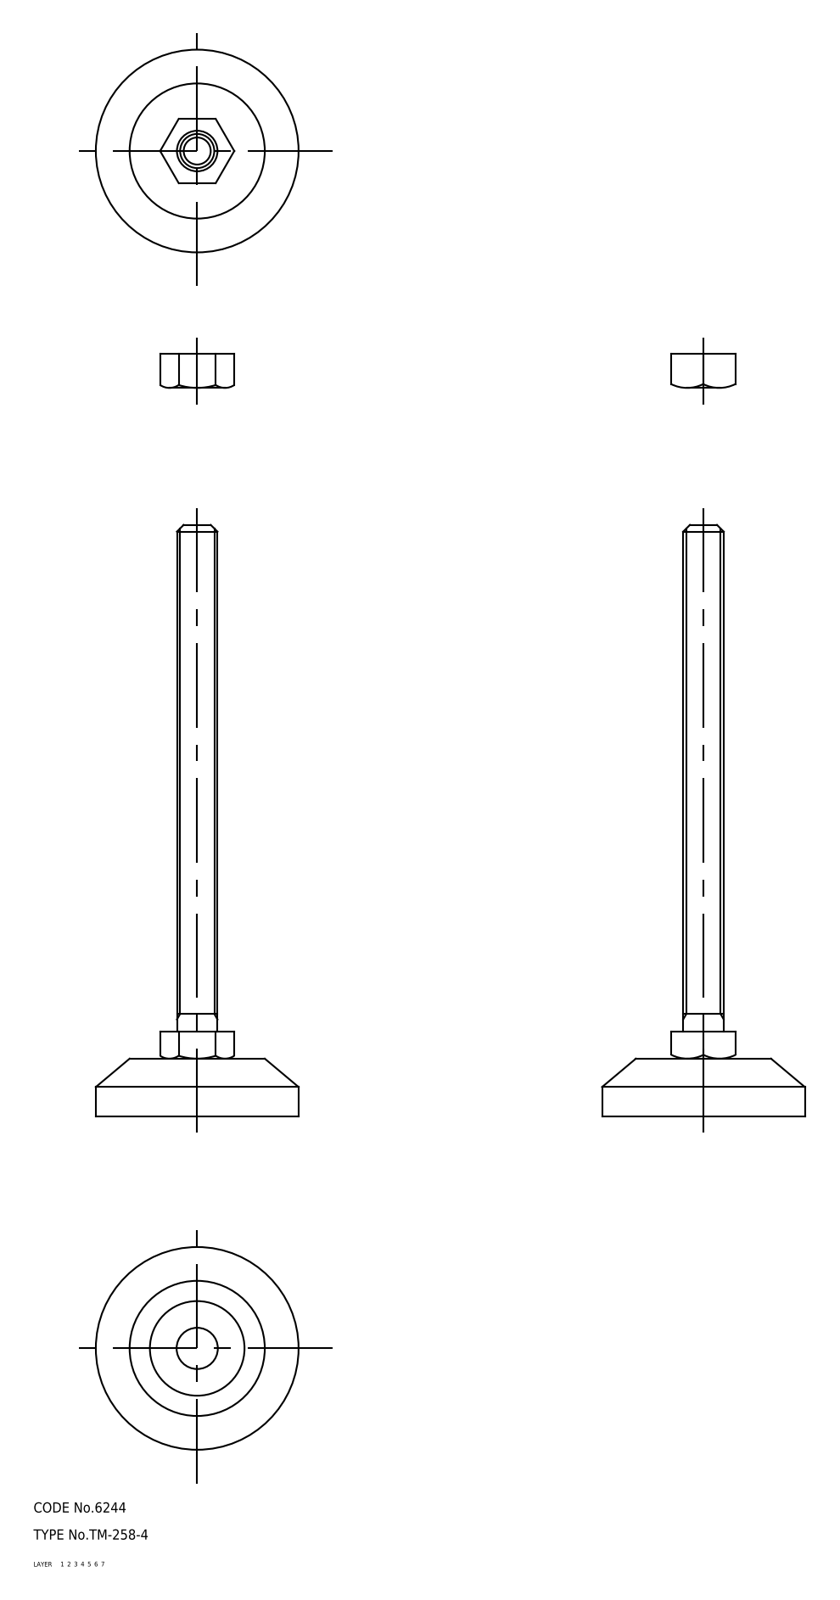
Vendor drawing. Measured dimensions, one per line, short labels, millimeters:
name: 67112543; 67112556; 67112569
written by: CADfix (AUTOMOTIVE_DESIGN)
unit: mm
bodies: 3 solids, 75 faces (0 planar, 0 cylindrical, 75 other)
size: 175 × 60 × 60
volume: 53 148 mm³; area: 17 458 mm²
